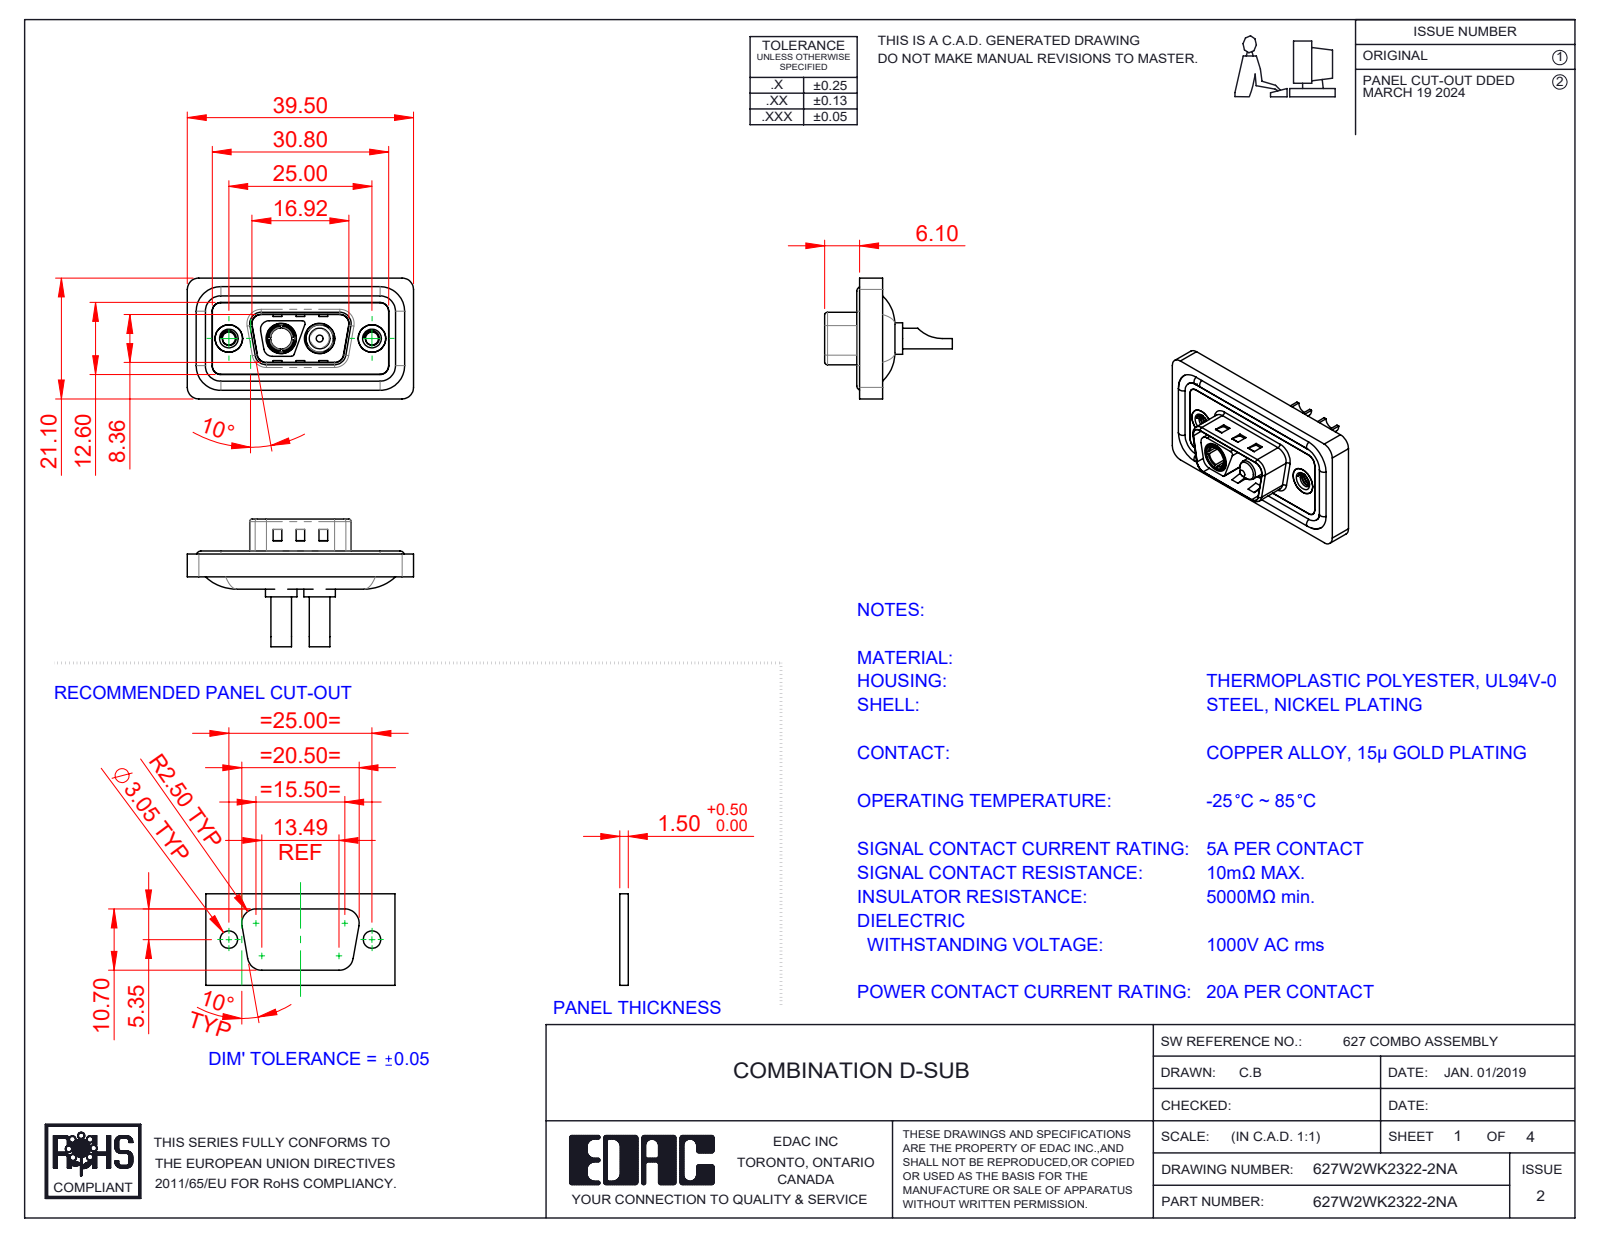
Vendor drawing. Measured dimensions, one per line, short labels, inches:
name: Power Pin_20A SC; Power Socket_20A SC; 627Combo Housing_2WK2; 627Combo Shell Rear_09 Contacts (+4 more)
written by: SolidWorks 2023 (CONFIG_CONTROL_DESIGN)
unit: in
bodies: 11 solids, 546 faces (195 planar, 235 cylindrical, 116 other)
size: 1.555 × 0.878 × 0.831
volume: 0.28 in³; area: 11.63 in²
holes: 2× ⌀0.089, 2× ⌀0.106, 2× ⌀0.157, 2× ⌀0.189, 2× ⌀0.191, 2× ⌀0.197, 2× ⌀0.209, 1× ⌀0.146
bosses: 4× ⌀0.063, 2× ⌀0.217, 2× ⌀0.205, 2× ⌀0.193, 2× ⌀0.187, 2× ⌀0.148, 2× ⌀0.142, 1× ⌀0.195
rounds: 24× R0.059, 18× R0.079, 10× R0.02, 8× R0.063, 4× R0.01, 4× R0.024, 4× R0.026, 4× R0.035
face distances: 0.016, 0.043, 0.114, 0.02, 0.122, 0.063, 0.059, 0.157, 0.098, 0.071
hole spacings: 0.36, 0.624, 0.265, 0.984
